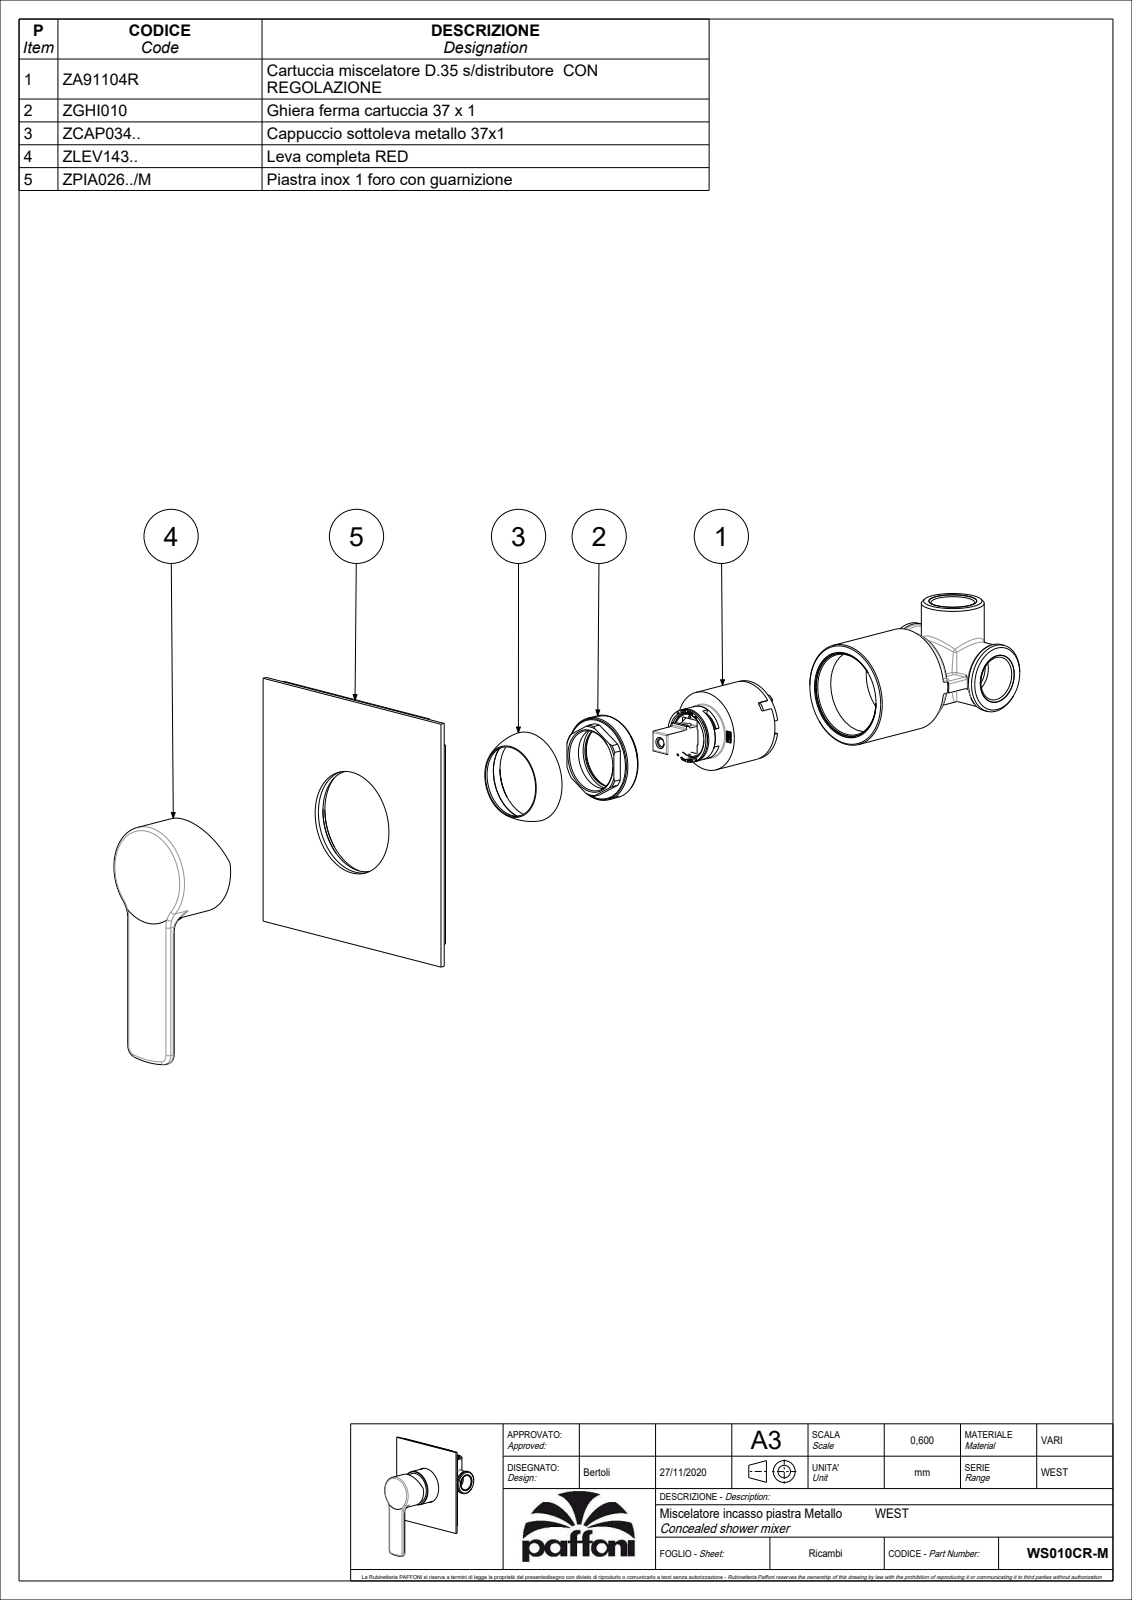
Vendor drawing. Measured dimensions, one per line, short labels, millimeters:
name: WS010CR-M
written by: CREO PARAMETRIC BY PTC INC, 2020044 (CONFIG_CONTROL_DESIGN)
unit: mm
bodies: 2 solids, 970 faces (559 planar, 228 cylindrical, 183 other)
size: 140 × 110 × 58.83
volume: 69 224 mm³; area: 57 108 mm²
holes: 2× ⌀3.3, 2× ⌀4, 1× ⌀3, 1× ⌀4.5, 1× ⌀5, 1× ⌀19.5, 1× ⌀19.9, 1× ⌀26.8, 1× ⌀29, 1× ⌀31, 1× ⌀32.4, 1× ⌀36
bosses: 1× ⌀44.8, 1× ⌀43, 1× ⌀35, 1× ⌀23.5, 1× ⌀23.4, 1× ⌀21.8, 1× ⌀7.6, 1× ⌀5.5
rounds: 45× R0.5, 11× R0.15, 4× R0.3, 4× R1.5, 2× R1, 2× R5, 2× R10, 1× R7
face distances: 2, 54.1, 52.1, 4.5, 58.6, 56.6, 5.5, 50.5, 59.5, 16.5
hole spacings: 12.5
